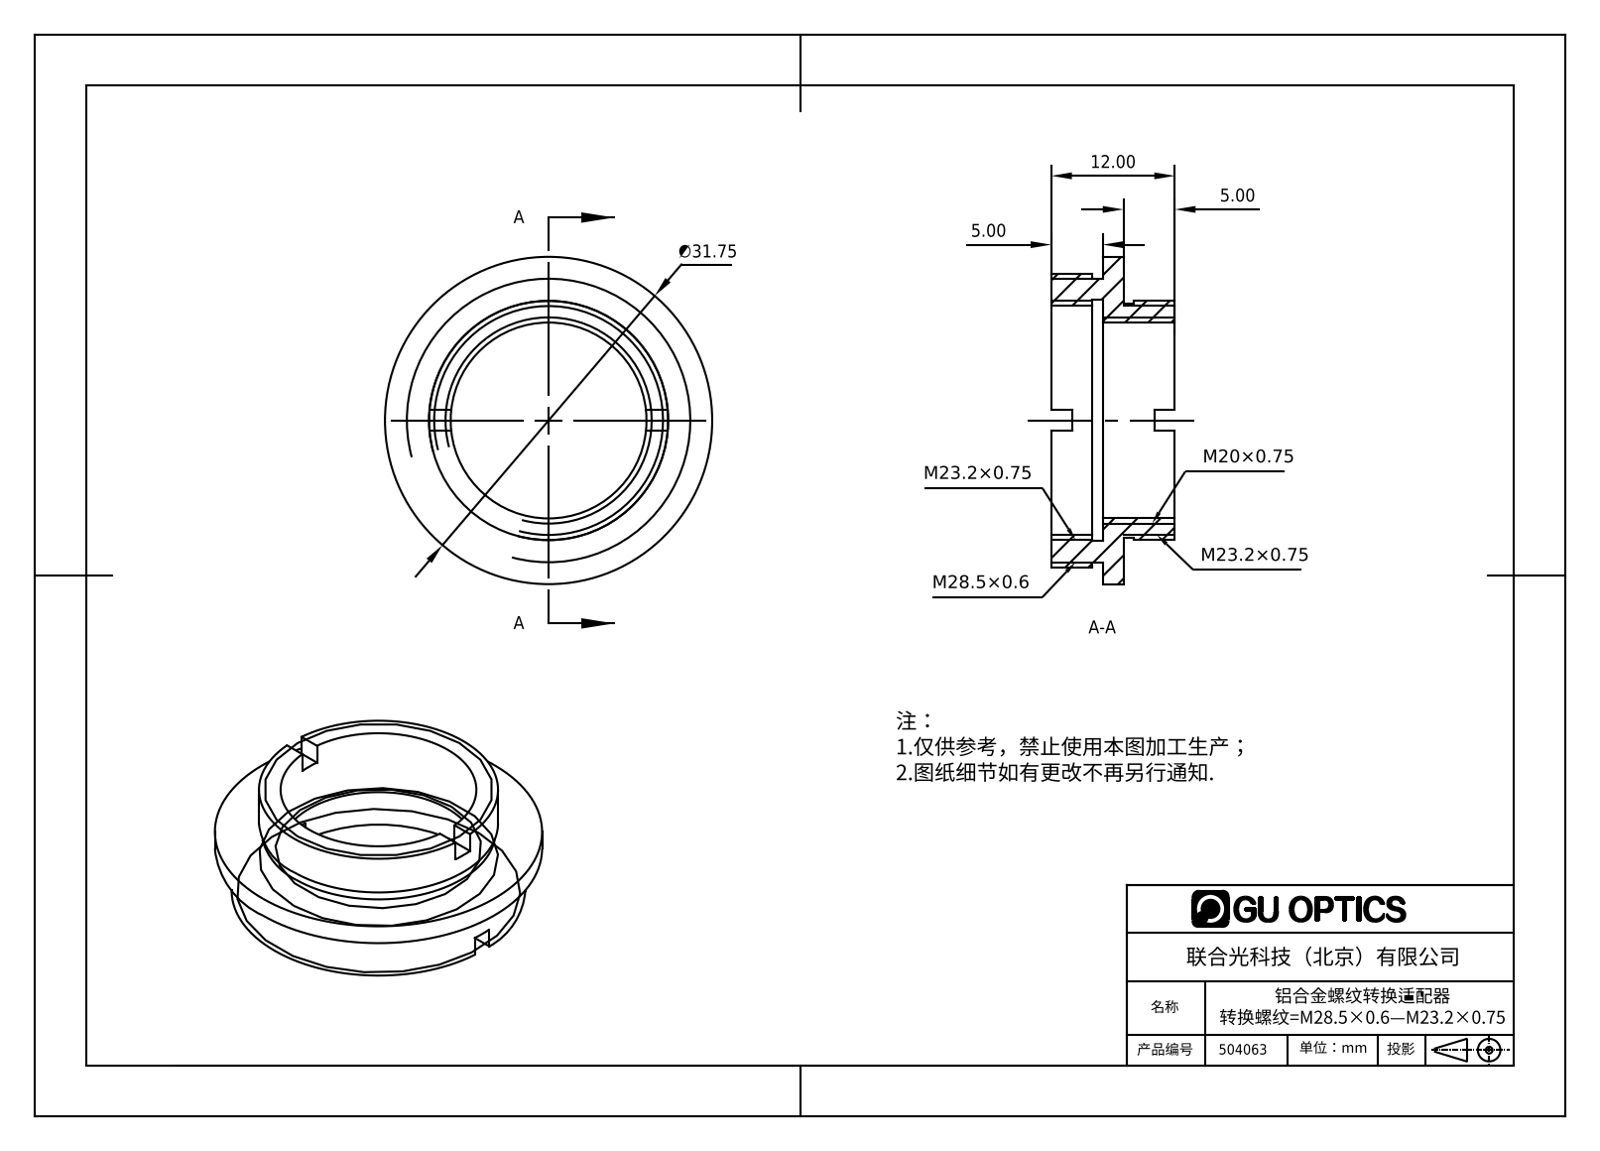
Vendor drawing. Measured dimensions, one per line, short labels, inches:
name: 504063
written by: SolidWorks 2016 (AUTOMOTIVE_DESIGN)
unit: in
bodies: 1 solid, 38 faces (22 planar, 16 cylindrical, 0 other)
size: 1.25 × 1.25 × 0.472
volume: 0.172 in³; area: 4.672 in²
holes: 1× ⌀0.748, 1× ⌀0.874, 1× ⌀0.921
bosses: 1× ⌀1.25, 1× ⌀1.122, 1× ⌀1.083, 1× ⌀0.913, 1× ⌀0.894
face distances: 0.079, 0.197, 0.276, 0.472, 0.118, 0.157, 0.315, 0.039, 0.394, 0.236
